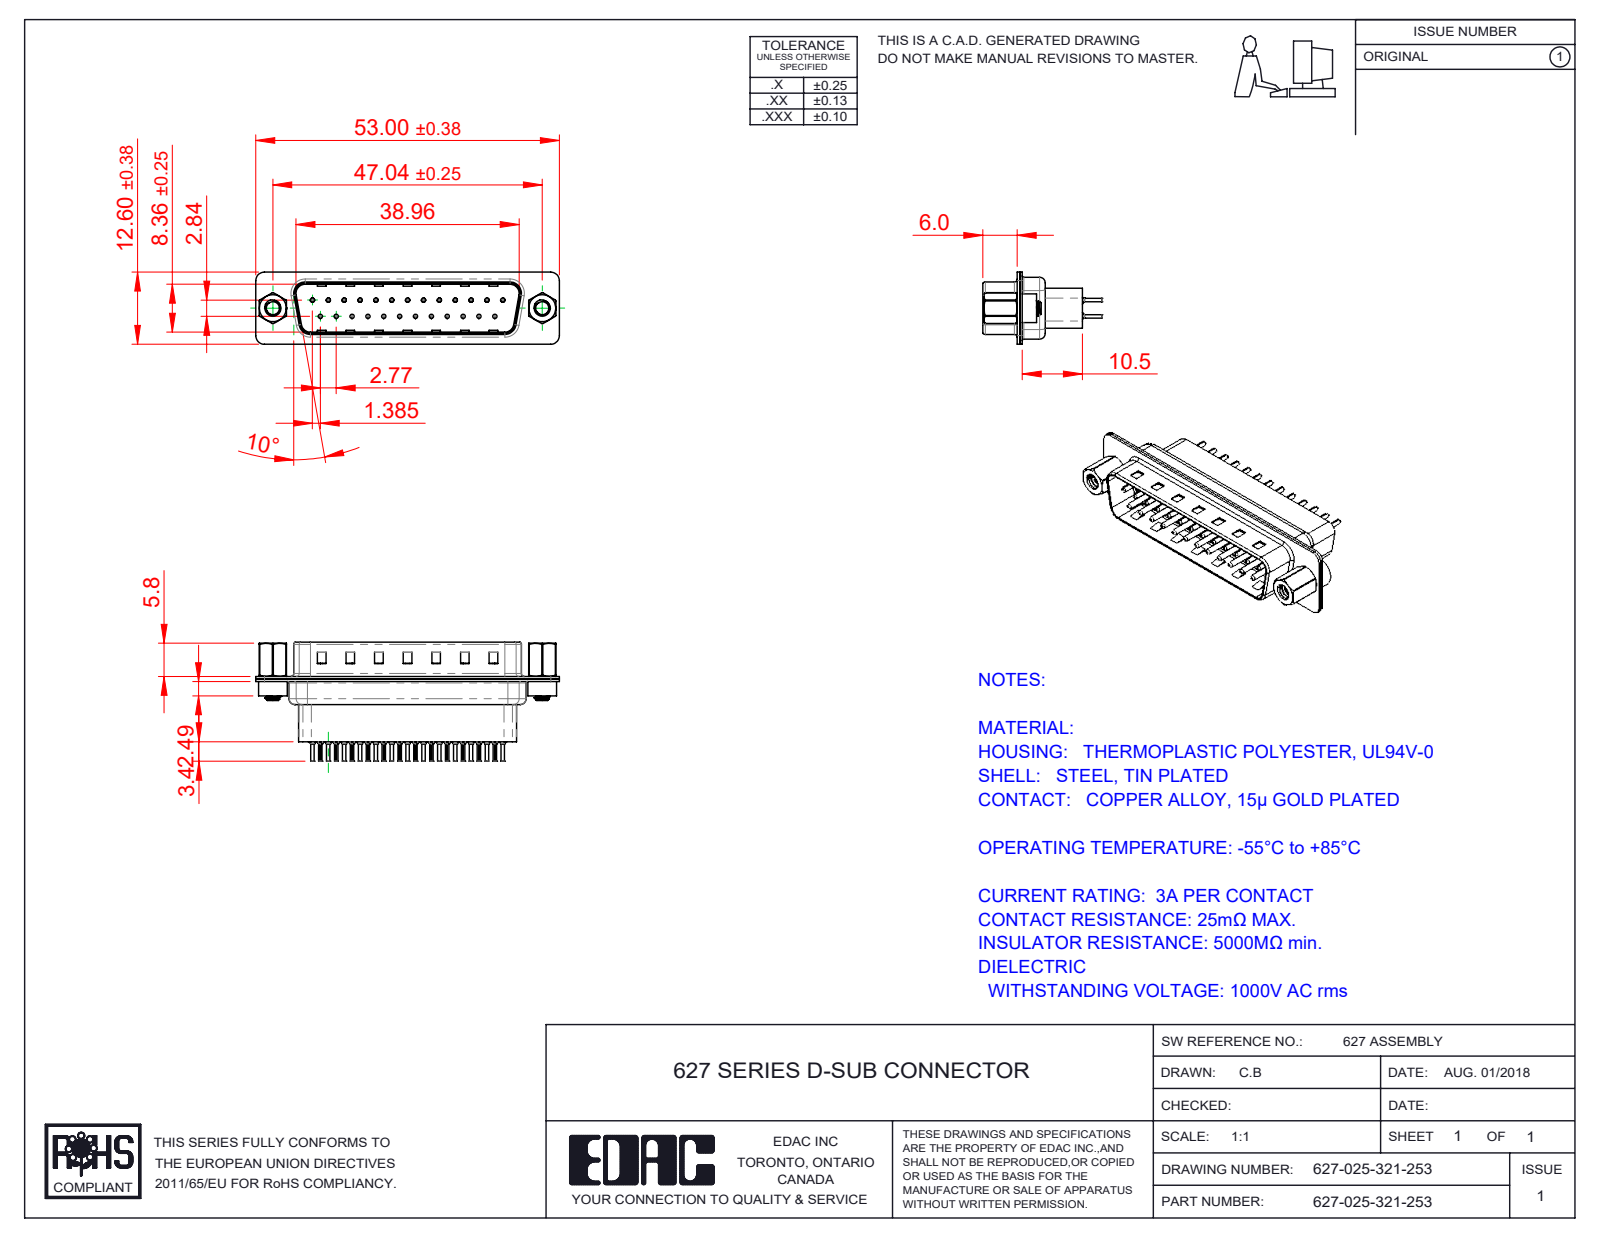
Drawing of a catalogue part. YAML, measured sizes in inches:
part_name: "627 Contact Row 2_21H; 627 4-40 Hex Standoff; 627 Housing_25 HP; 627 Shell Front_25 Contacts (+4 more)"
step_written_by: "SolidWorks 2020 (CONFIG_CONTROL_DESIGN)"
units: inches
bodies: {solids: 32, faces: 2948, planar: 793, cylindrical: 1132, other: 1023}
overall_size: [2.087, 0.819, 0.496]
volume: 0.244
surface_area: 15.89
round_holes:
  - {diameter: 0.008, count: 25}
  - {diameter: 0.014, count: 25}
  - {diameter: 0.043, count: 25}
  - {diameter: 0.063, count: 25}
  - {diameter: 0.089, count: 2}
  - {diameter: 0.09, count: 2}
  - {diameter: 0.157, count: 2}
  - {diameter: 0.189, count: 2}
round_bosses_or_shafts:
  - {diameter: 0.079, count: 25}
  - {diameter: 0.059, count: 25}
  - {diameter: 0.03, count: 25}
  - {diameter: 0.024, count: 25}
  - {diameter: 0.197, count: 2}
  - {diameter: 0.193, count: 2}
  - {diameter: 0.11, count: 2}
partial_cylinders:
  - {radius: 0.004, count: 50}
  - {radius: 0.059, count: 16}
  - {radius: 0.079, count: 12}
  - {radius: 0.02, count: 8}
  - {radius: 0.063, count: 8}
  - {radius: 0.01, count: 4}
  - {radius: 0.024, count: 4}
  - {radius: 0.026, count: 4}
face_to_face_distances: [0.016, 0.018, 0.032, 0.377, 0.027, 0.302, 0.059, 0.035, 0.043, 0.318]
hole_center_spacings: [0.124, 0.327, 0.109, 0.218, 0.436, 0.654, 0.198, 0.198]
